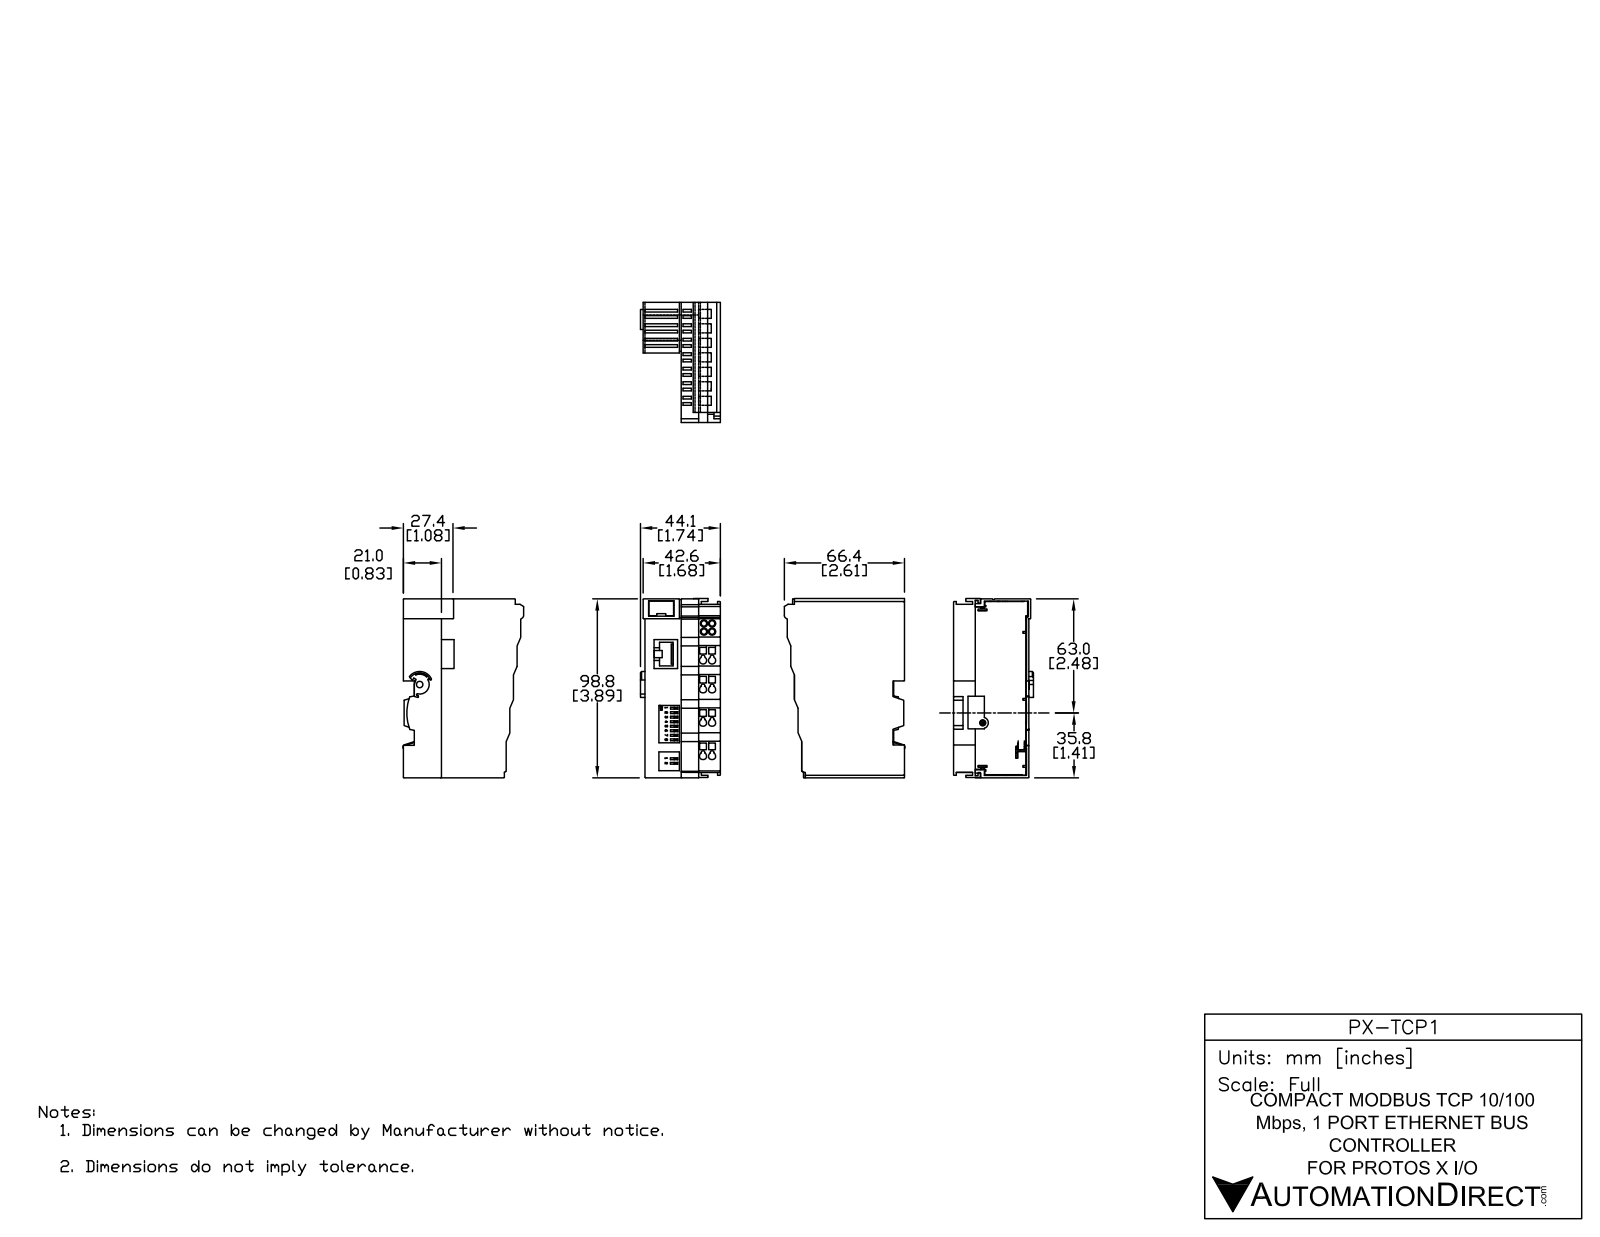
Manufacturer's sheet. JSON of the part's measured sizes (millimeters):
{"part_name": "PX-TCP1", "step_written_by": "SolidWorks 2014 (AUTOMOTIVE_DESIGN)", "units": "millimeters", "bodies": {"solids": 45, "faces": 2099, "planar": 1570, "cylindrical": 421, "other": 108}, "overall_size": [100.25, 69.31, 44.25], "volume_mm3": 79550, "surface_area_mm2": 73155, "round_holes": [[4, 8], [3.75, 2]], "partial_cylinders_radius": [[0.25, 77], [0.3, 47], [1, 20], [0.4, 18], [0.38, 12], [2, 12], [0.17, 4], [0.5, 4]], "face_to_face_distances": [1, 8, 13, 20, 12, 21, 9, 7, 28, 29], "hole_center_spacings": [5, 18.4, 19.07, 16, 16.76, 34.4, 34.76, 36.8]}
